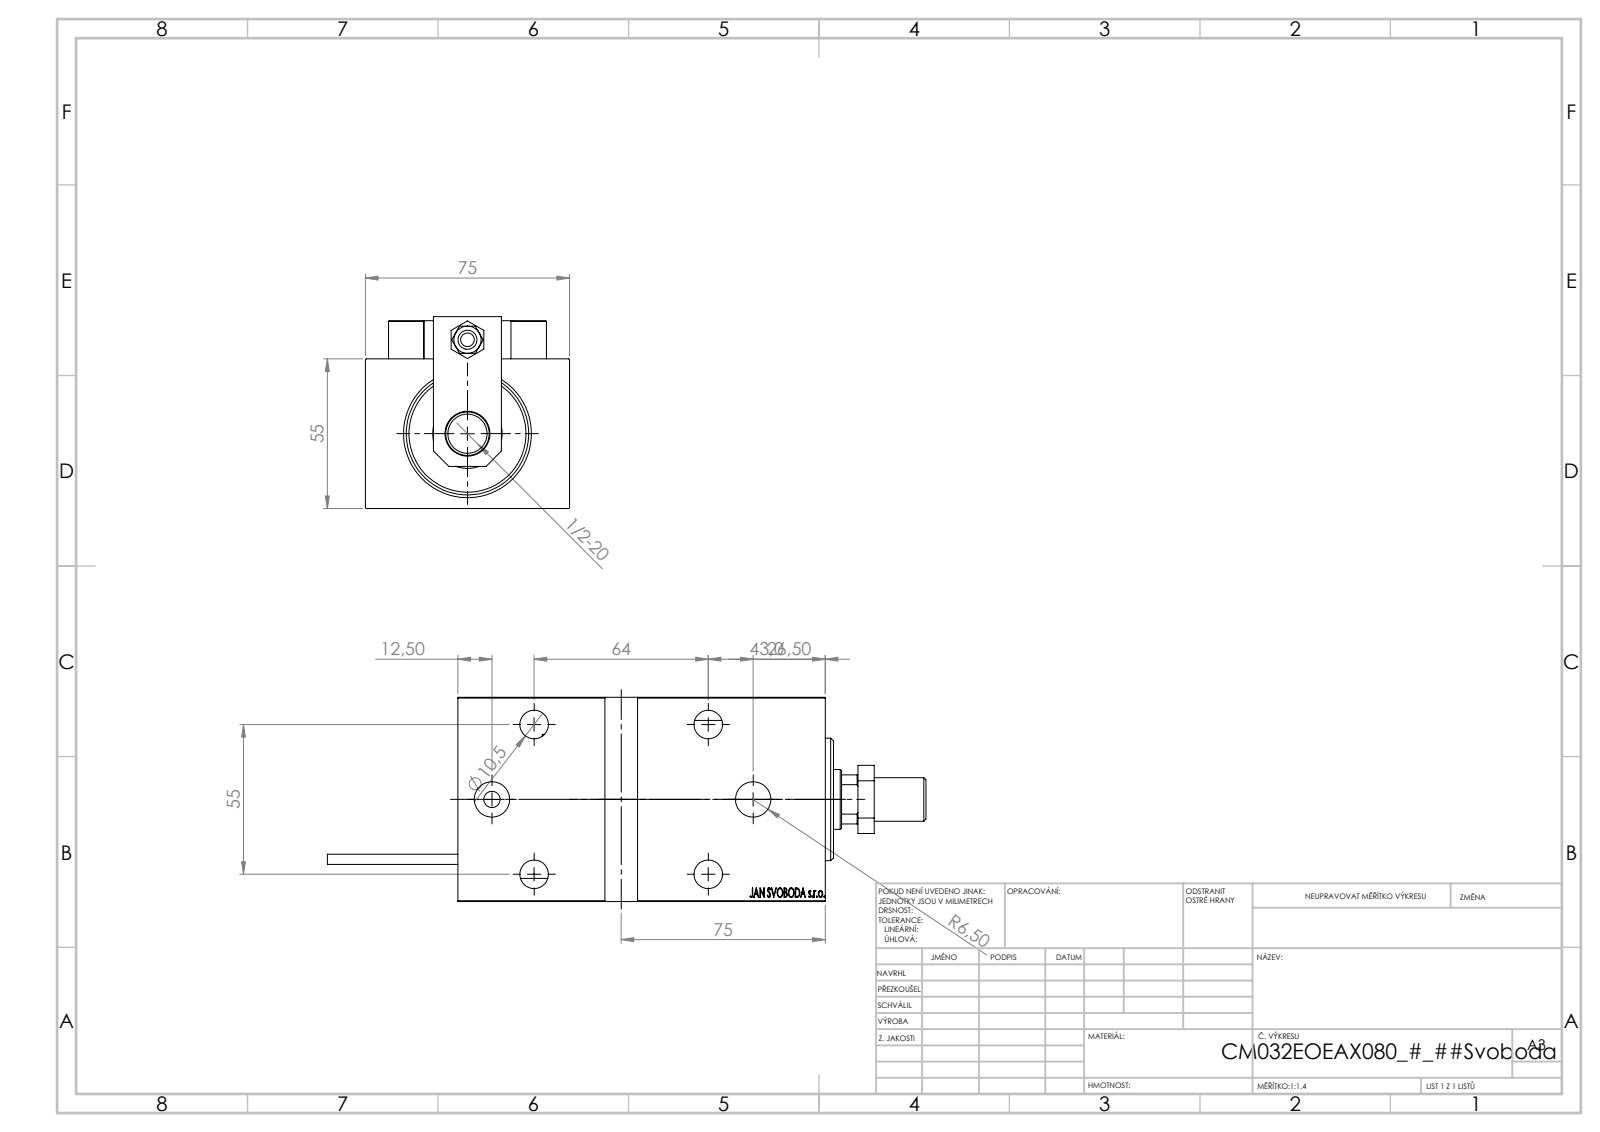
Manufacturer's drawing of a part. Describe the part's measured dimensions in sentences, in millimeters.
The part is named "ALLEN BOLT D8; Block; SWITCH X; V450CM_E_VCP (+7 more)". Its 3-D file was written by "SolidWorks 2019 (CONFIG_CONTROL_DESIGN)". It is 25 solids with 1296 faces: 571 planar, 178 cylindrical and 547 other. Overall it measures 220 by 75 by 70.5 millimeters. Its volume is 557 335 cubic millimeters and its surface area 110 597 square millimeters. Round holes: 5 of diameter 8, 5 of diameter 10.5, 5 of diameter 16.5, 4 of diameter 3.2, 4 of diameter 4, 2 of diameter 5, 2 of diameter 13, 1 of diameter 7, 1 of diameter 22, 1 of diameter 25.5, 1 of diameter 32, 1 of diameter 45. Round bosses or shafts: 2 of diameter 5, 2 of diameter 3.8, 1 of diameter 34, 1 of diameter 16, 1 of diameter 14, 1 of diameter 13, 1 of diameter 11, 1 of diameter 6. Partial cylindrical surfaces (rounded edges, fillets, slot ends): 30 of radius 0.3, 2 of radius 3, 1 of radius 10.5. The main face-to-face distances are 55, 75, 10, 69, 14, 3, 135, 12, 25, 125. The hole center spacings are 11.37, 12.5, 20, 21.91, 28.9, 29.59, 29.69, 31.57.
